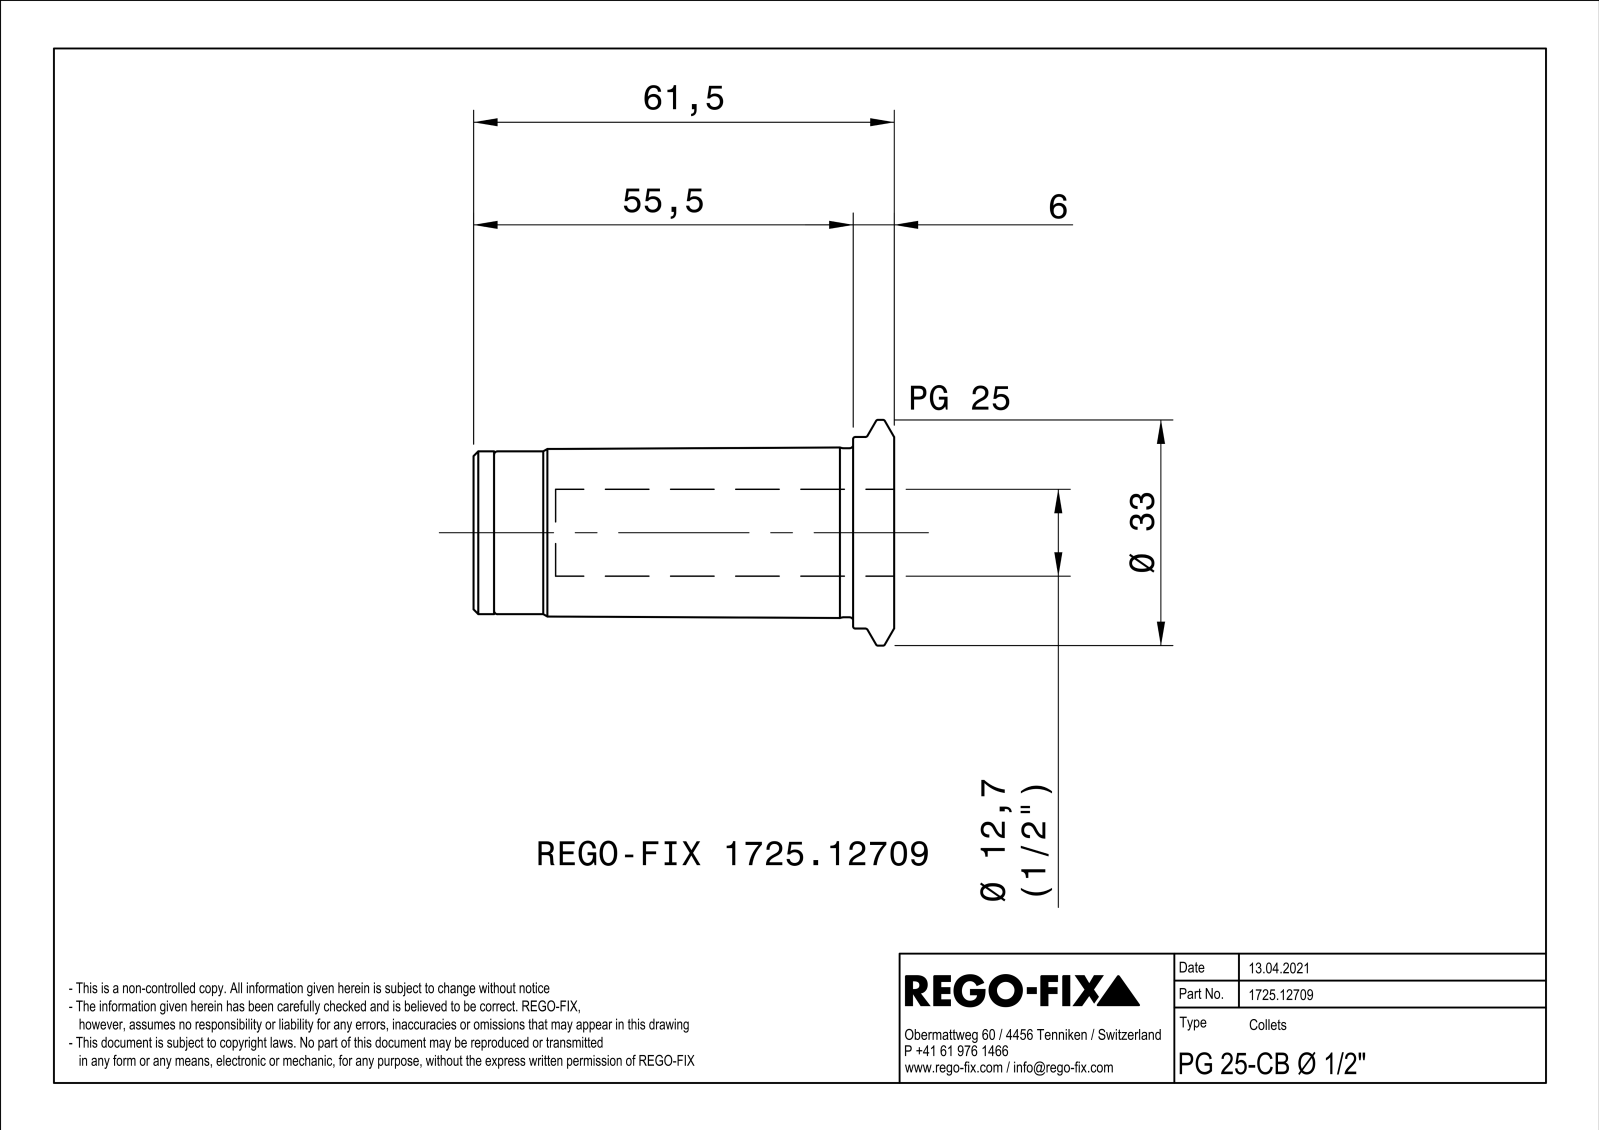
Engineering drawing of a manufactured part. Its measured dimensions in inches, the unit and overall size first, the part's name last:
Units: inches
Overall size (bounding box): 2.382 × 1.299 × 1.299
Round holes (diameter × count): ⌀0.059 ×3, ⌀0.098 ×3, ⌀0.205 ×1, ⌀0.272 ×1, ⌀0.323 ×1, ⌀0.5 ×1, ⌀0.824 ×1, ⌀0.874 ×1
Round bosses / shafts (diameter × count): ⌀1.299 ×1, ⌀1.102 ×1, ⌀0.972 ×1, ⌀0.937 ×1, ⌀0.866 ×1, ⌀0.803 ×1, ⌀0.472 ×1
Partial cylindrical surfaces — rounded edges, fillets, slot ends (radius × count): R0.059 ×3
Main face-to-face distances: 0.039, 2.382, 2.071, 0.311, 2.303, 0.232, 0.079, 1.969, 0.102, 0.335
Hole centre spacings: 0.302, 0.299, 0.305, 0.518, 0.604, 0.302, 0.529, 0.528
Volume: 0.166 in³ · Surface area: 19.17 in²
Bodies: 1 solid, 94 faces (20 planar, 29 cylindrical, 45 other)
Part name (STEP PRODUCT): NOCUT
STEP written by: SIEMENS PLM Software Solid Edge ST10 (AUTOMOTIVE_DESIGN)
